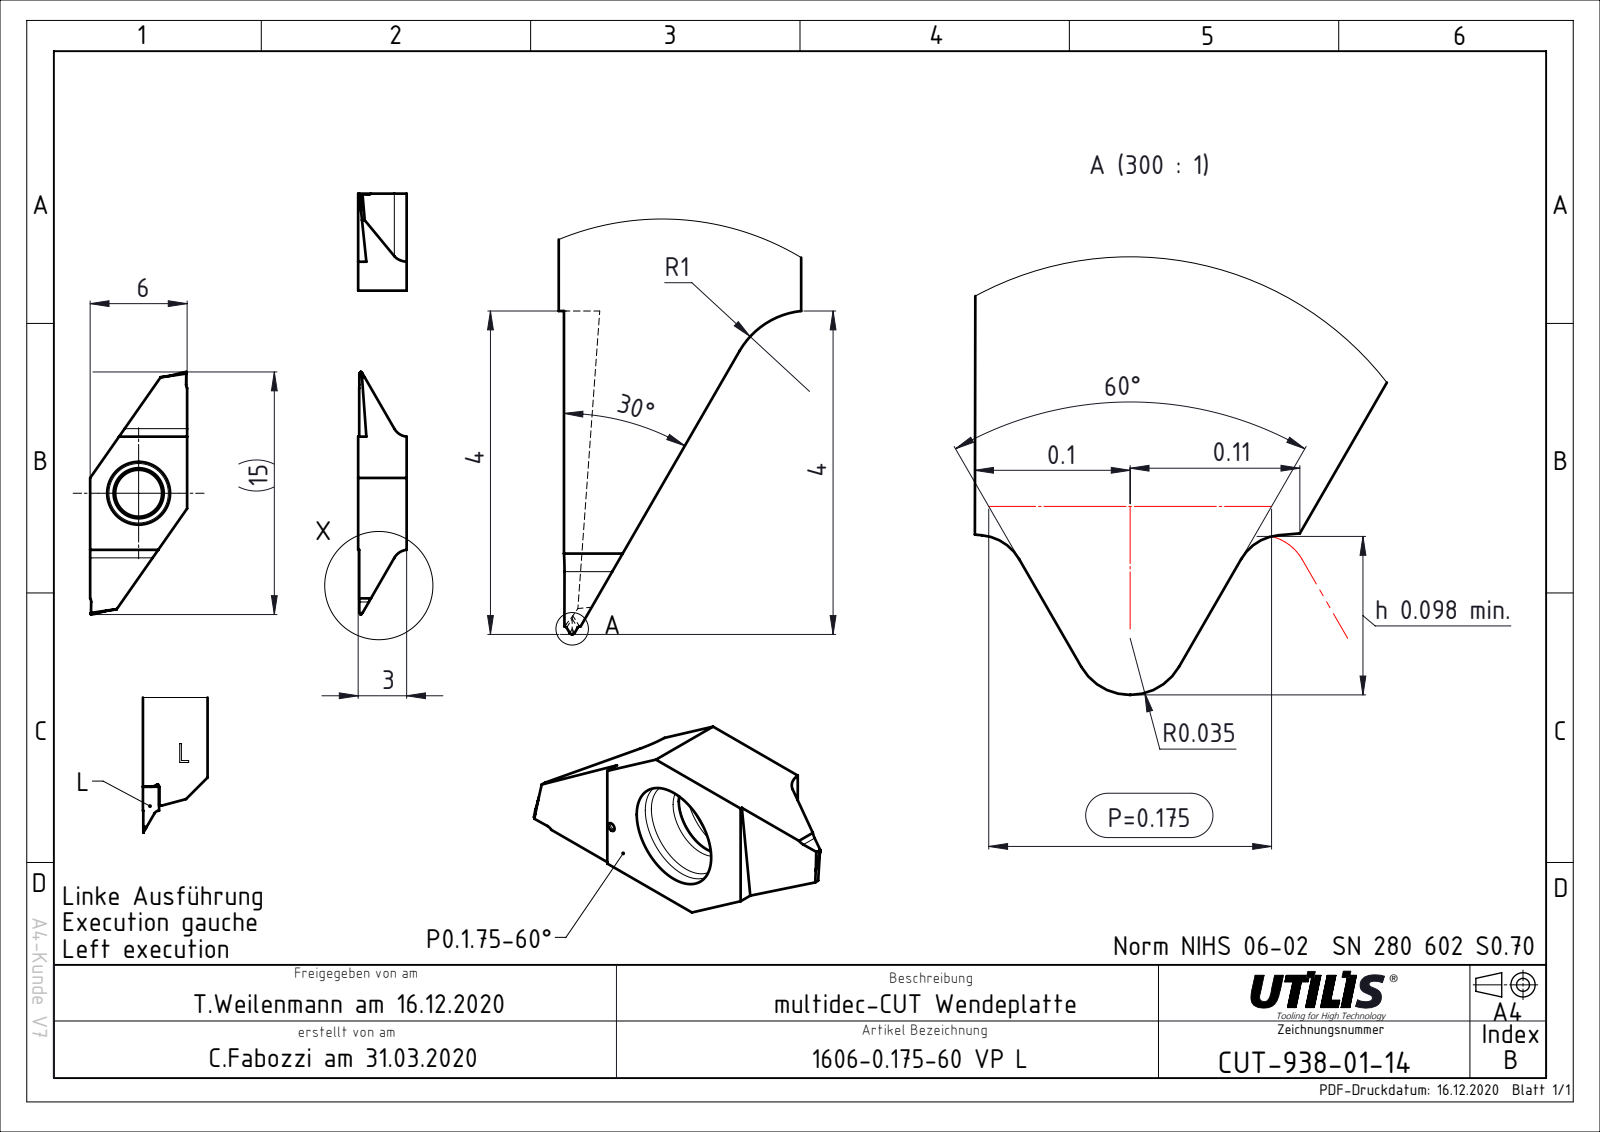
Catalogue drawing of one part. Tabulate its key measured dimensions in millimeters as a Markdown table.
| quantity | value |
| --- | --- |
| part name | CUT-938-01; ASME Y14.5 |
| STEP written by | FormatWorks Professional (AP242_MANAGED_MODEL_BASED_3D_ENGINEERING_MIM_LF) |
| units | millimeters |
| bodies | 1 solid, 36 faces (22 planar, 14 cylindrical, 0 other) |
| overall size | 15 × 6 × 3 |
| volume | 125 mm³ |
| surface area | 209 mm² |
| round holes (diameter × count) | 2.9 × 1 |
| partial cylindrical surfaces (radius × count) | 1 × 2 |
| main face-to-face distances | 6, 3, 9, 7, 12, 7.22, 7.21, 14.44, 14.43 |
